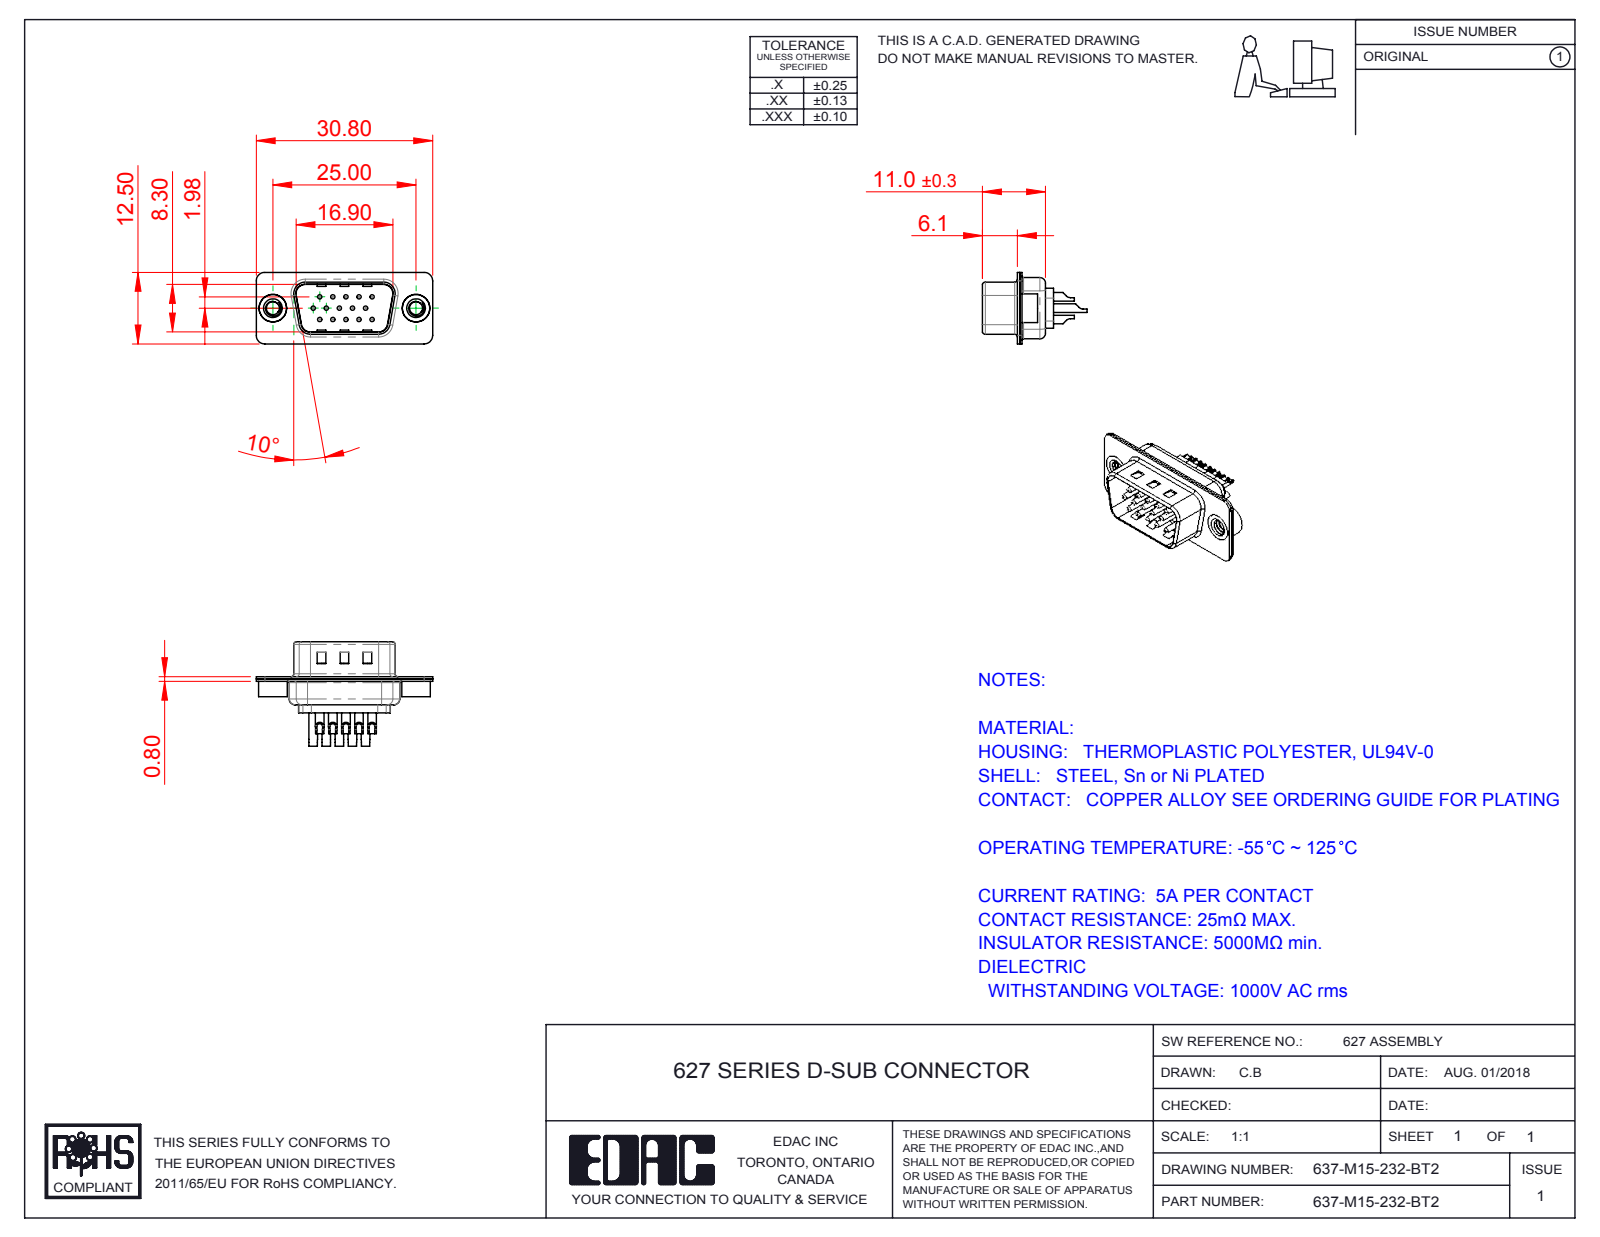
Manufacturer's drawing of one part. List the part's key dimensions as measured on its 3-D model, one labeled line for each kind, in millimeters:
Part name (STEP PRODUCT): 637M Contact Row 1_32; 637M Contact Row 2_32; 637M 4-40 Threaded Rivet; 637M Housing_15 Contacts (+4 more)
STEP written by: SolidWorks 2016 (CONFIG_CONTROL_DESIGN)
Units: millimetres
Bodies: 20 solids, 859 faces (242 planar, 369 cylindrical, 248 other)
Overall size (bounding box): 30.8 × 18.25 × 12.5
Volume: 1 398 mm³ · Surface area: 4 275 mm²
Round holes (diameter × count): ⌀0.75 ×15, ⌀1 ×15, ⌀1.6 ×15, ⌀2 ×15, ⌀2.26 ×2, ⌀4 ×2, ⌀4.8 ×2
Round bosses / shafts (diameter × count): ⌀1.5 ×15, ⌀5 ×2, ⌀4.9 ×2
Partial cylindrical surfaces — rounded edges, fillets, slot ends (radius × count): R1.5 ×16, R2 ×12, R0.5 ×8, R1.6 ×8, R1 ×7, R0.25 ×4, R0.6 ×4, R0.65 ×4
Main face-to-face distances: 0.4, 0.8, 9.5, 9.1, 0.65, 8.7, 9.9, 1.4, 0.75, 0.35
Hole centre spacings: 3.96, 2.28, 2.29, 4.57, 6.05, 6.86, 7.92, 6.04
